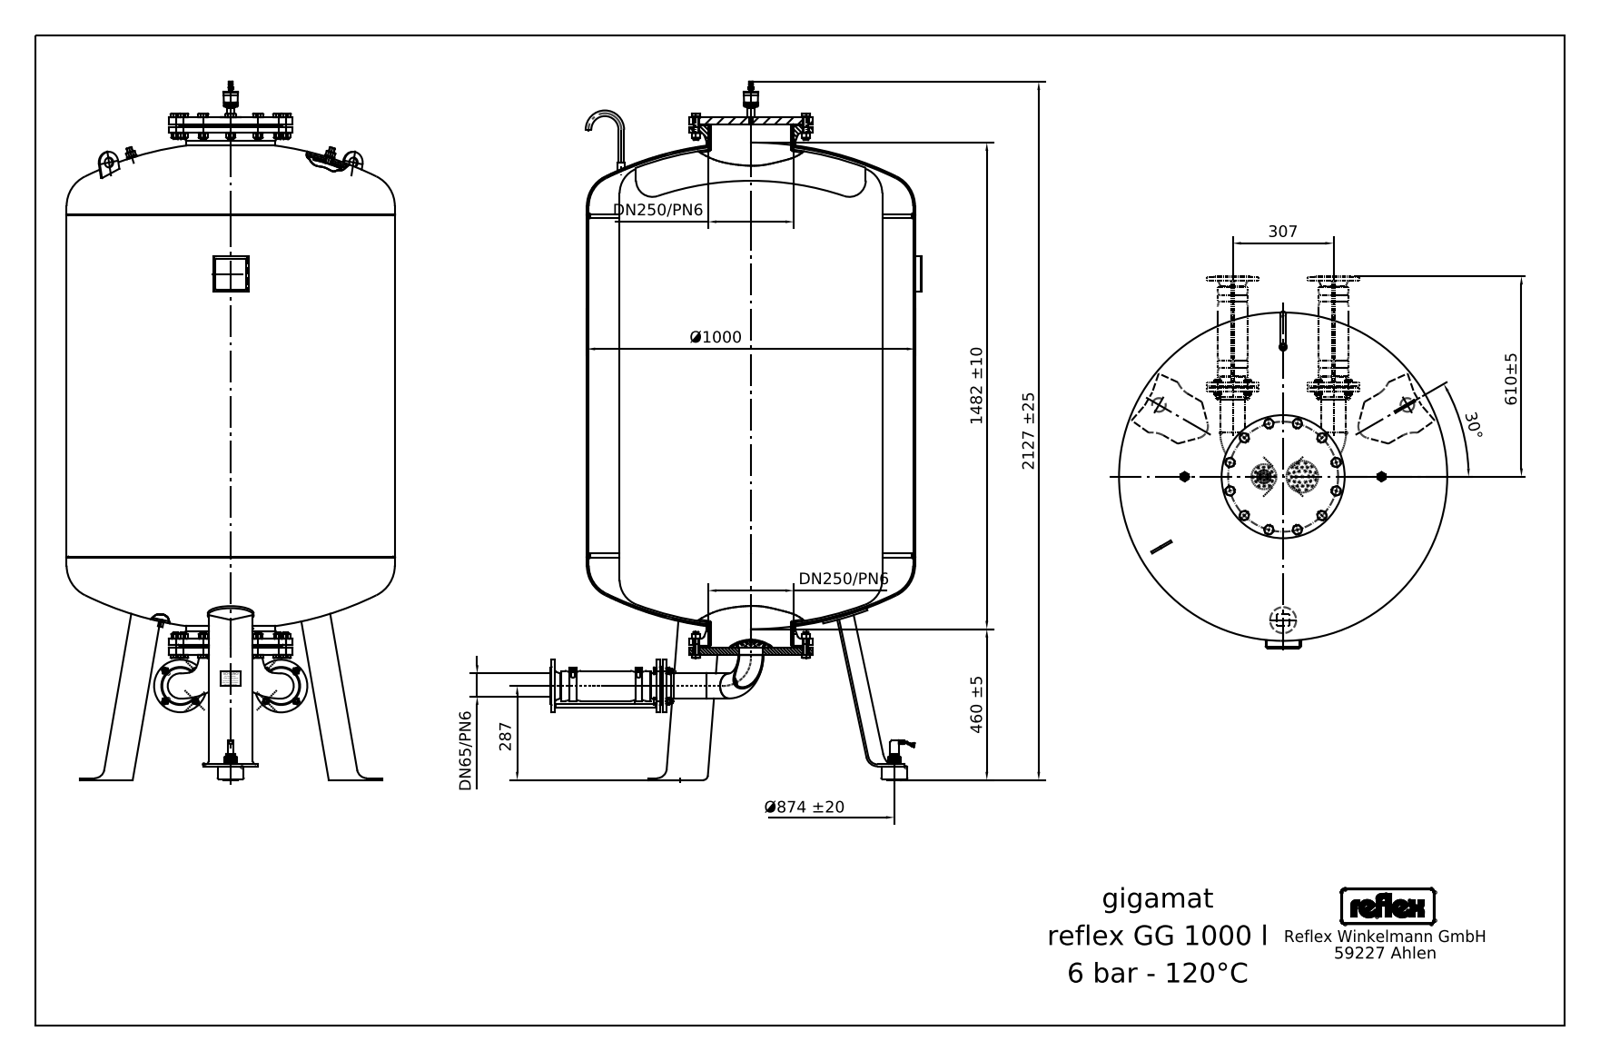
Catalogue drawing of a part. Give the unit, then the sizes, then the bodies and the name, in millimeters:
Units: millimetres
Overall size (bounding box): 2127 × 1108.35 × 1000
Round holes (diameter × count): ⌀14 ×8, ⌀8 ×1, ⌀30 ×1, ⌀70.3 ×1, ⌀76.1 ×1, ⌀260.4 ×1
Round bosses / shafts (diameter × count): ⌀16 ×24, ⌀160 ×2, ⌀96.1 ×2, ⌀86.1 ×2, ⌀76.1 ×2, ⌀16.6 ×2, ⌀12 ×2, ⌀10 ×2
Partial cylindrical surfaces — rounded edges, fillets, slot ends (radius × count): R25 ×18, R2 ×8, R8.44 ×4, R3.38 ×3, R5.76 ×2, R9 ×2, R10.12 ×2, R13.91 ×2
Main face-to-face distances: 1045, 22, 297.5, 1342.5, 1591, 27, 275.5, 1320.5, 1618, 1640
Hole centre spacings: 65, 91.92, 307, 129.99, 265.06, 320.47, 355.94, 175.78
Volume: 1 081 000 000 mm³ · Surface area: 11 100 000 mm²
Bodies: 24 solids, 1074 faces (567 planar, 268 cylindrical, 239 other)
STEP written by: Mechanical Desktop 2008 (CONFIG_CONTROL_DESIGN)
